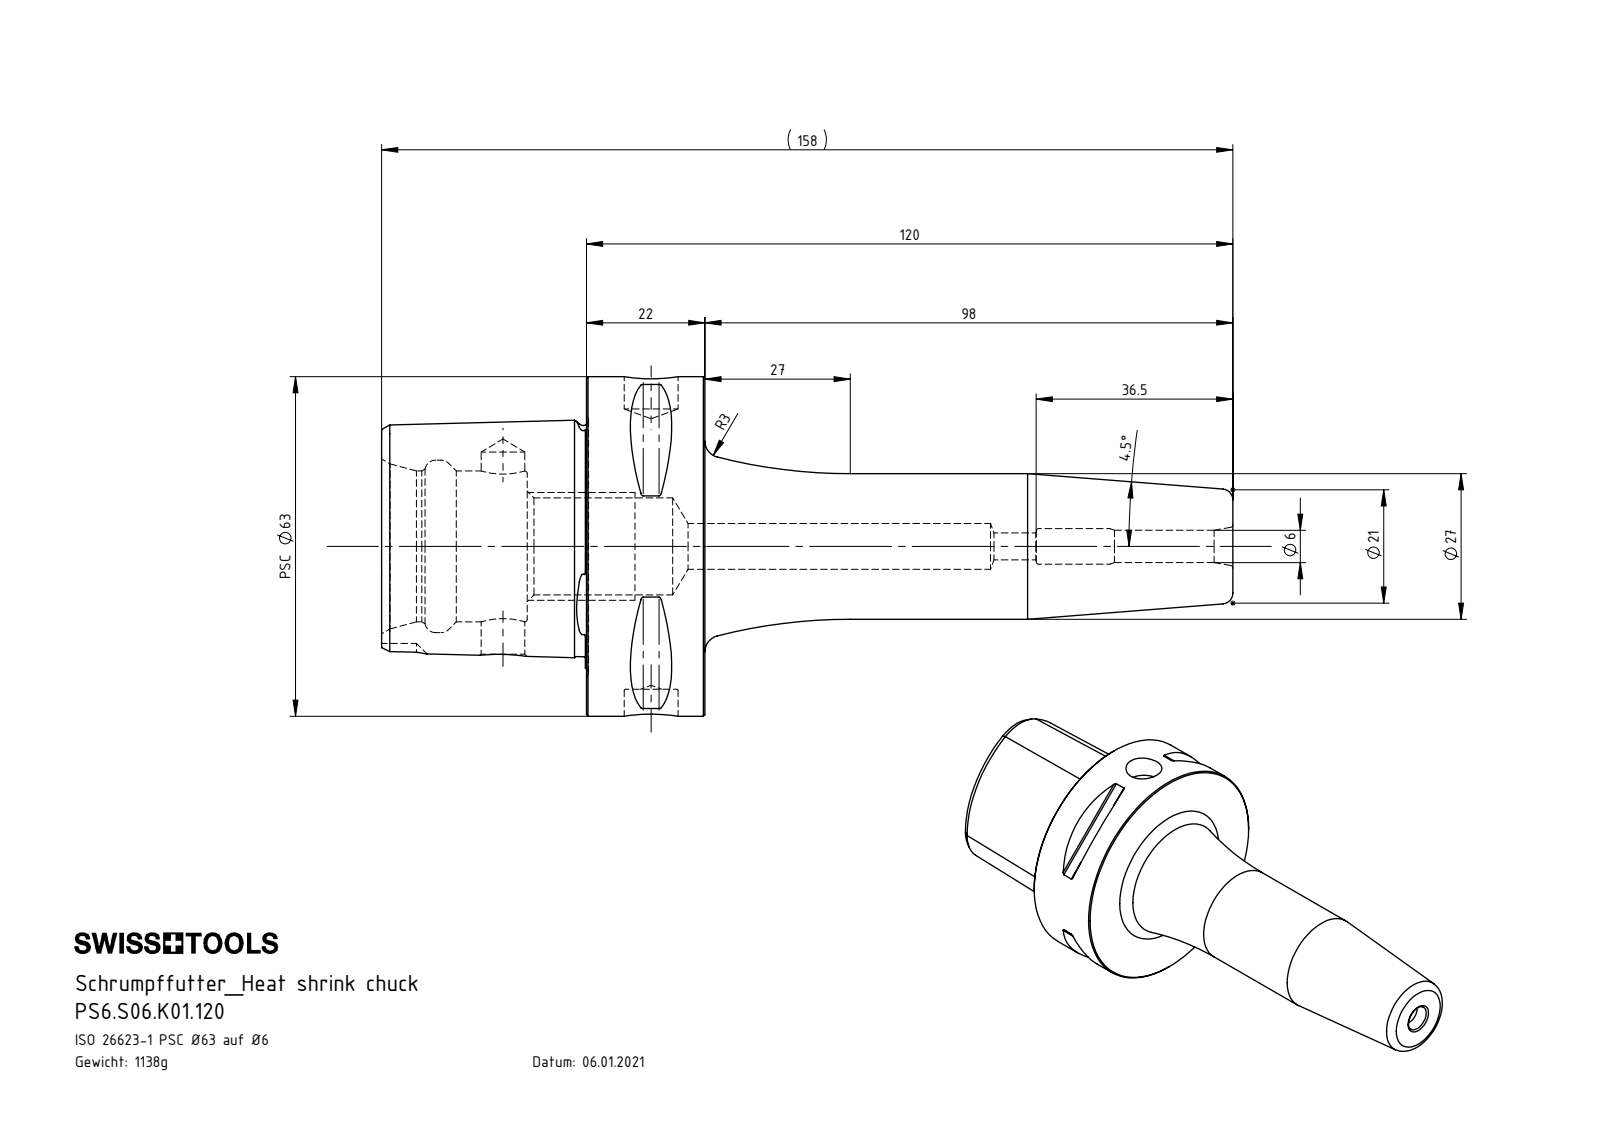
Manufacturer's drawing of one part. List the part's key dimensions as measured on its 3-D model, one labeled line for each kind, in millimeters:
Part name (STEP PRODUCT): PS6.S06.K01.120
STEP written by: SolidWorks 2022 (AUTOMOTIVE_DESIGN)
Units: millimetres
Bodies: 1 solid, 158 faces (22 planar, 37 cylindrical, 99 other)
Overall size (bounding box): 158 × 63 × 63
Volume: 144 976 mm³ · Surface area: 30 090 mm²
Round holes (diameter × count): ⌀5 ×1, ⌀6 ×1, ⌀6.6 ×1, ⌀8.1 ×1, ⌀8.5 ×1, ⌀10 ×1, ⌀18 ×1, ⌀28 ×1, ⌀32 ×1
Round bosses / shafts (diameter × count): ⌀63 ×1, ⌀27 ×1
Partial cylindrical surfaces — rounded edges, fillets, slot ends (radius × count): R0.5 ×8, R6 ×1
Main face-to-face distances: 22, 38, 60, 24.88, 27, 11, 33, 158, 131, 120
Hole centre spacings: 27.5
